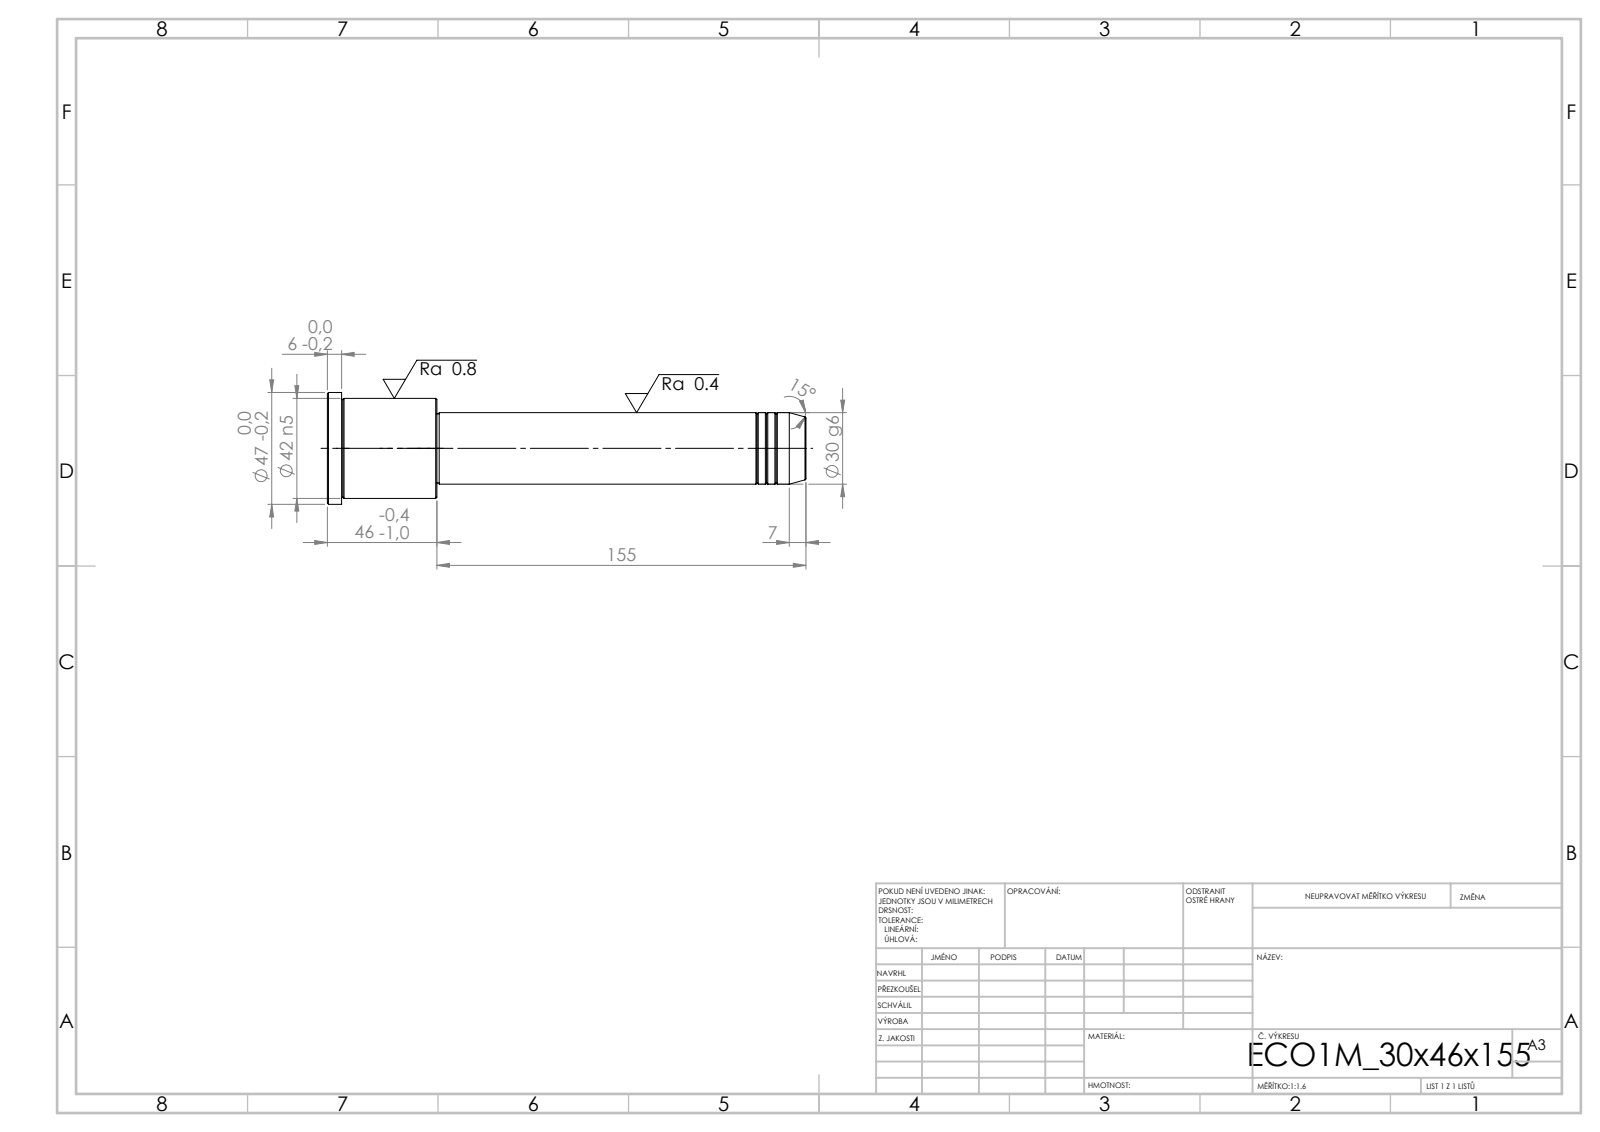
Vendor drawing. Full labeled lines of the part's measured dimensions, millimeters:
STEP written by: SolidWorks 2019 (CONFIG_CONTROL_DESIGN)
Units: millimetres
Bodies: 1 solid, 43 faces (5 planar, 14 cylindrical, 24 other)
Overall size (bounding box): 201 × 47 × 47
Volume: 174 553 mm³ · Surface area: 24 279 mm²
Round bosses / shafts (diameter × count): ⌀47 ×1, ⌀42 ×1, ⌀30 ×1, ⌀29 ×1
Main face-to-face distances: 46, 155, 201, 195, 40, 6, 154, 1, 41, 47
